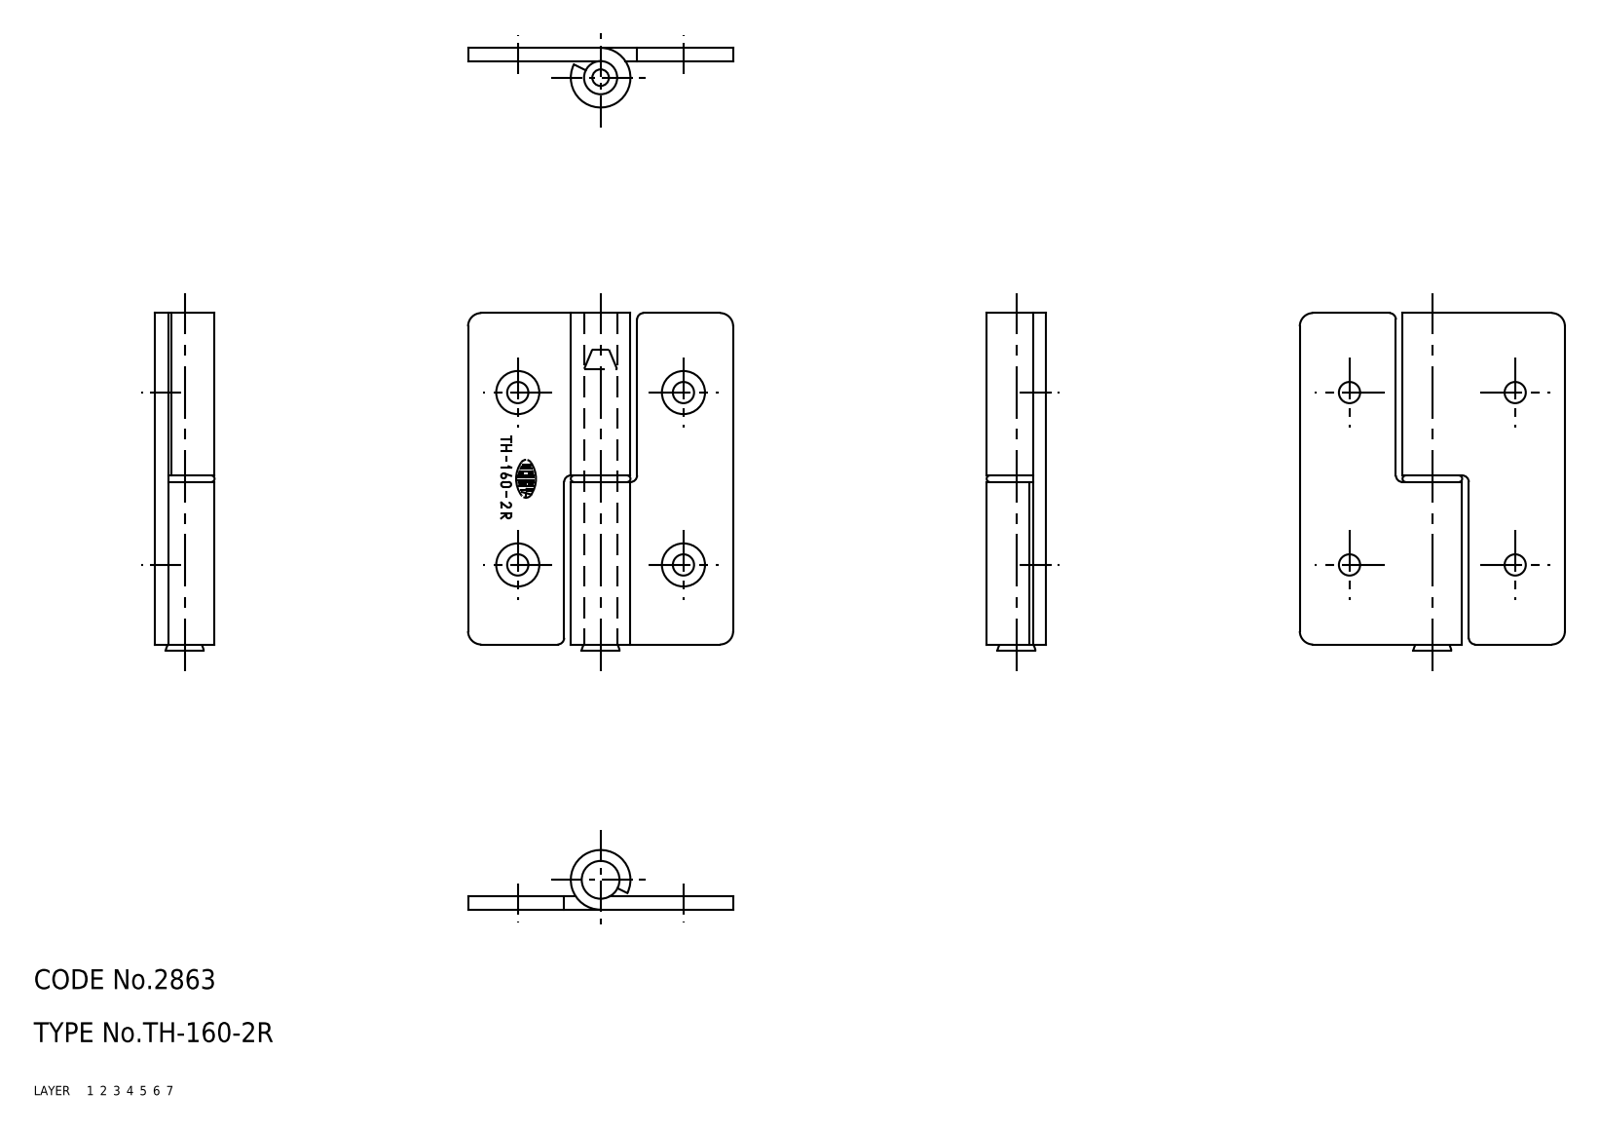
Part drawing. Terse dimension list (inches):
name: 67112596; 67112609; 67112622
written by: CADfix (AUTOMOTIVE_DESIGN)
unit: in
bodies: 3 solids, 60 faces (0 planar, 0 cylindrical, 60 other)
size: 2.008 × 1.575 × 0.354
volume: 0.365 in³; area: 10.42 in²
